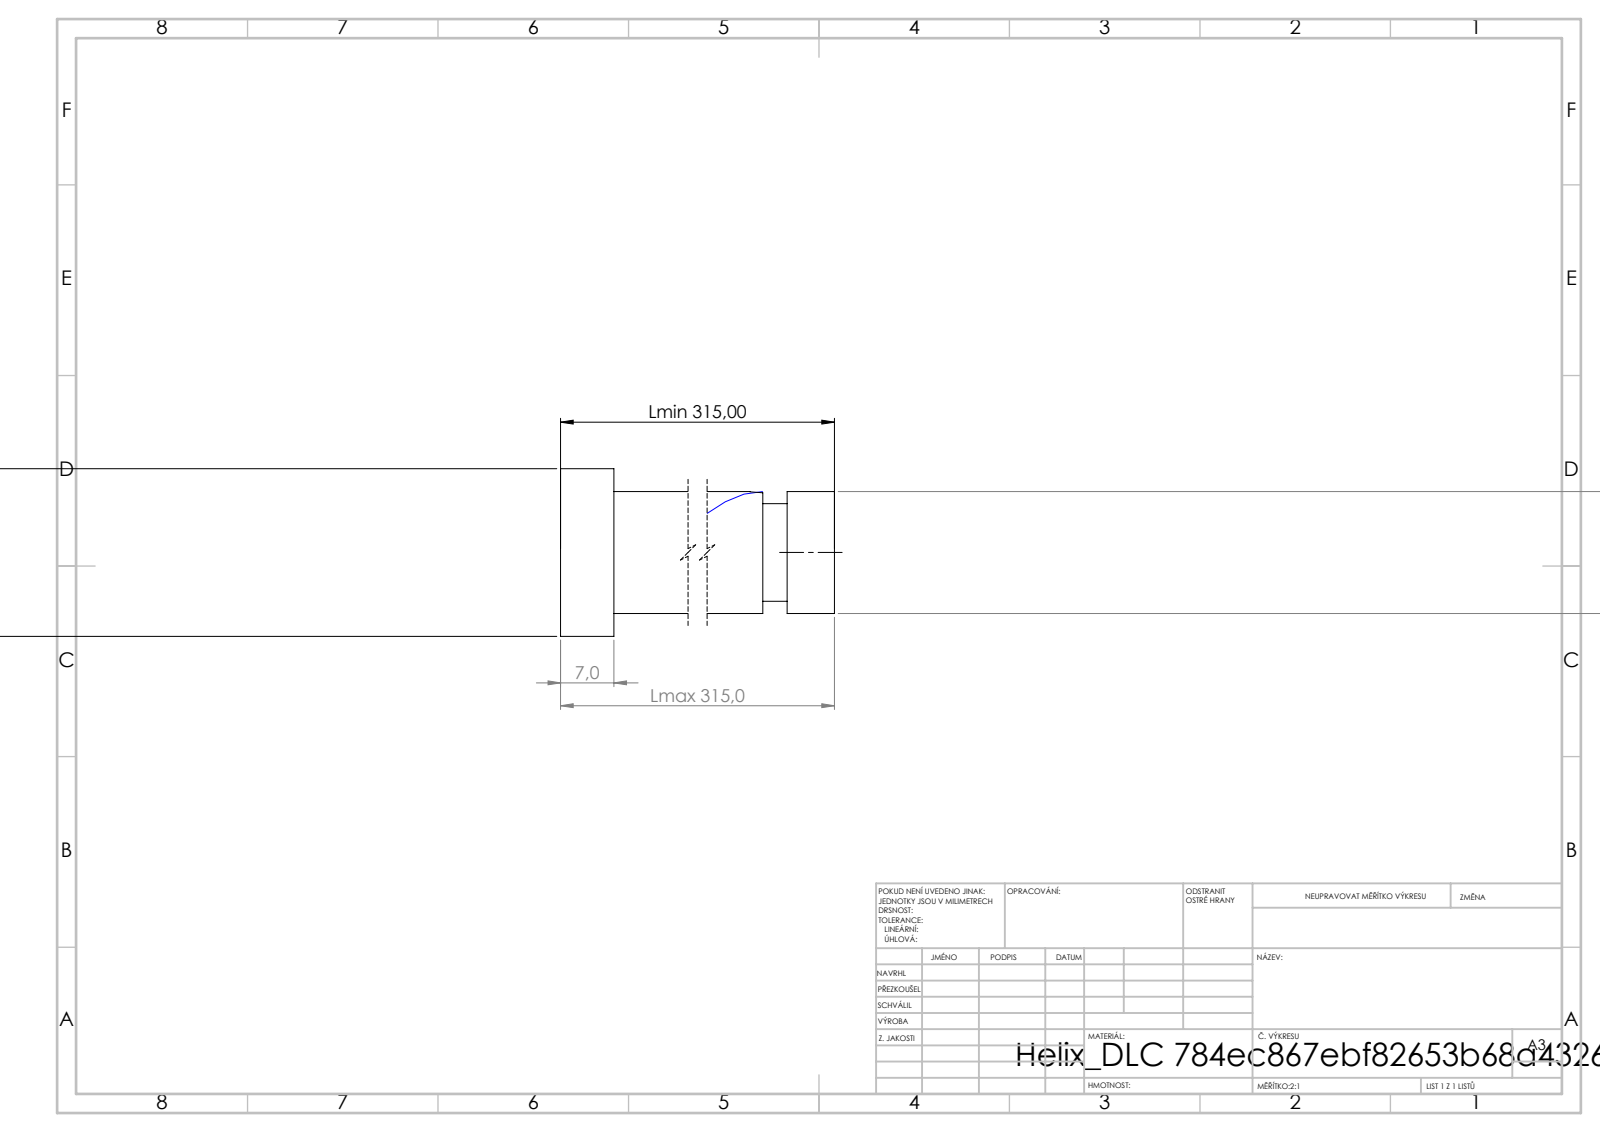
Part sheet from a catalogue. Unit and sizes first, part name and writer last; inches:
Units: inches
Overall size (bounding box): 12.402 × 0.866 × 0.866
Round bosses / shafts (diameter × count): ⌀0.866 ×1, ⌀0.63 ×1, ⌀0.504 ×1
Main face-to-face distances: 12.402, 0.276, 12.126, 12.157, 11.881, 0.244, 12.031, 11.756, 0.126, 0.37
Volume: 3.89 in³ · Surface area: 26.68 in²
Bodies: 1 solid, 21 faces (6 planar, 14 cylindrical, 1 other)
STEP written by: SolidWorks 2019 (CONFIG_CONTROL_DESIGN)
